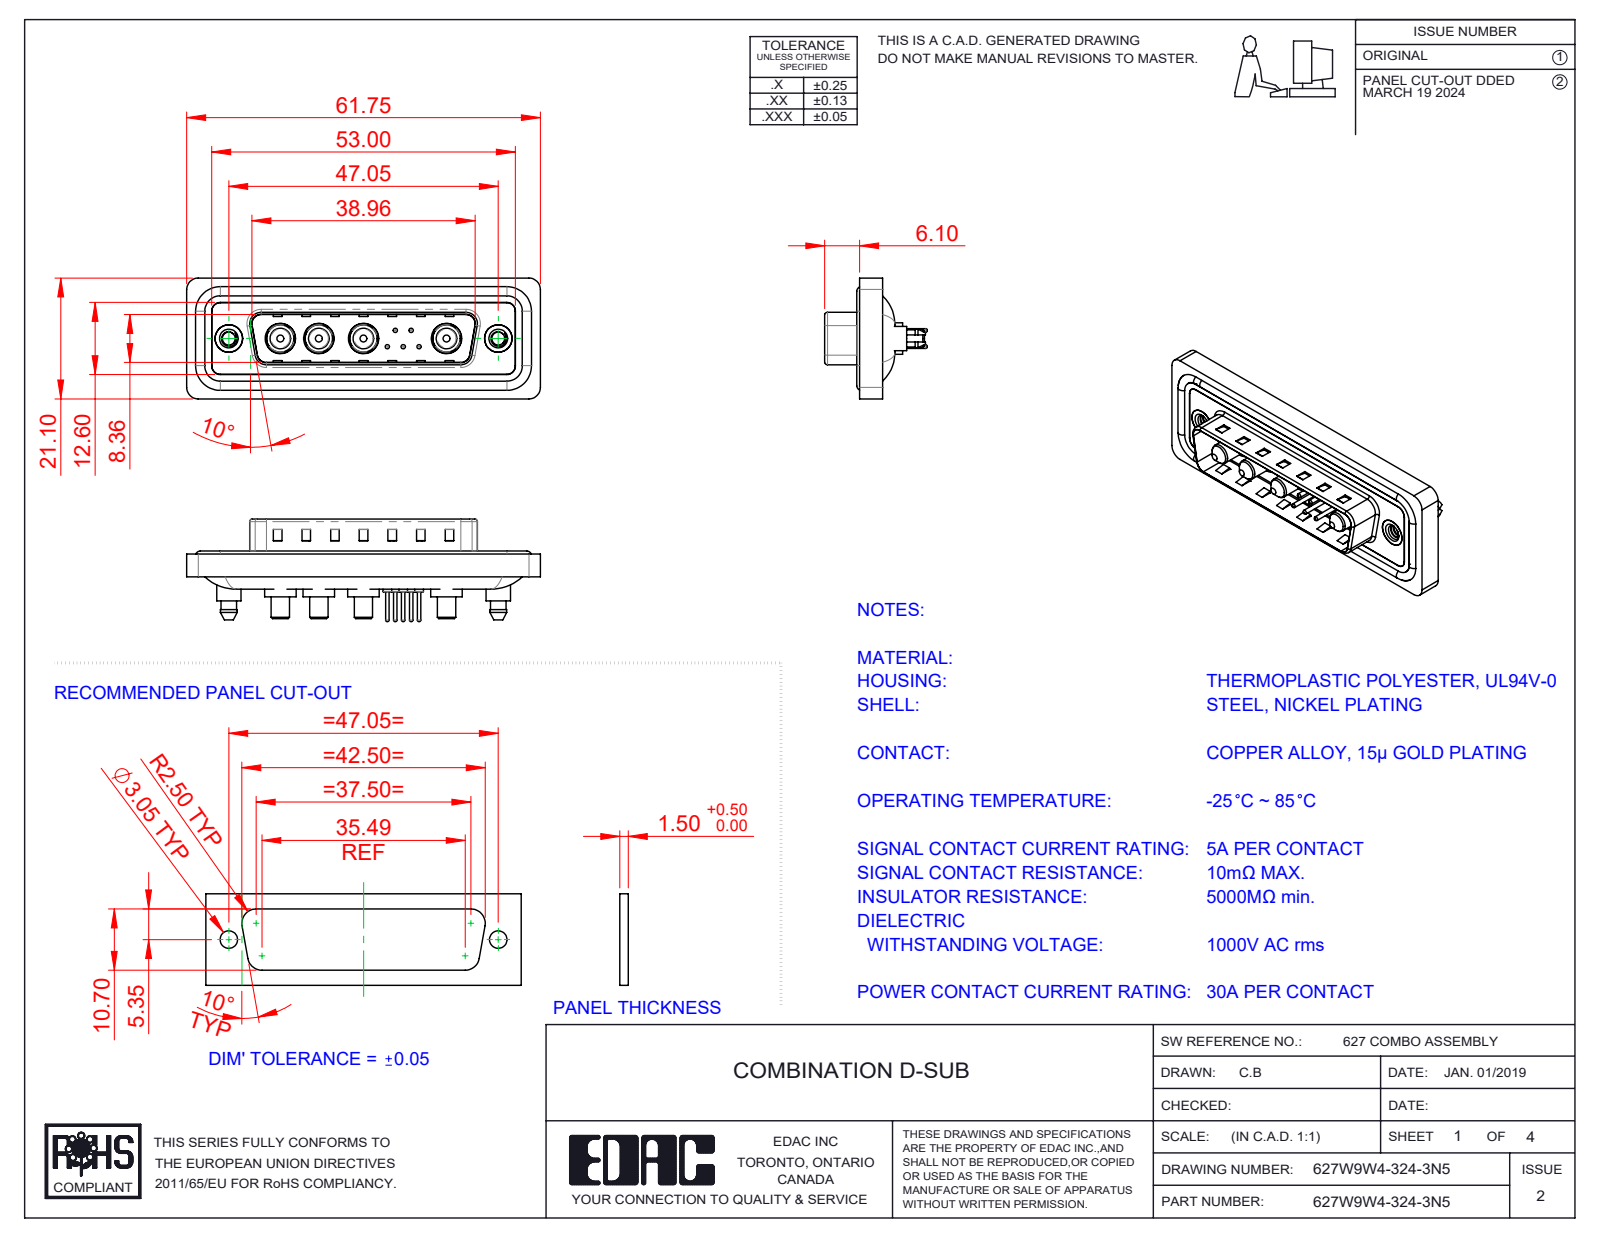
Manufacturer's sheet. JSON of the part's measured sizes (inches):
{"part_name": "Power Pin_30A S; 627Combo Shell Rear_25 Contacts; 627W9W4-324-3N5; 627Combo Contact Row 1_24 (+5 more)", "step_written_by": "SolidWorks 2023 (CONFIG_CONTROL_DESIGN)", "units": "inches", "bodies": {"solids": 20, "faces": 874, "planar": 300, "cylindrical": 366, "other": 208}, "overall_size": [2.431, 0.831, 0.705], "volume_in3": 0.462, "surface_area_in2": 18.89, "round_holes": [[0.03, 5], [0.063, 5], [0.079, 5], [0.191, 4], [0.209, 4], [0.089, 2], [0.157, 2], [0.189, 2], [0.197, 2]], "round_bosses_or_shafts": [[0.059, 5], [0.024, 5], [0.217, 4], [0.205, 4], [0.187, 4], [0.148, 4], [0.142, 4], [0.126, 4]], "partial_cylinders_radius": [[0.059, 24], [0.079, 18], [0.063, 10], [0.02, 8], [0.01, 4], [0.024, 4], [0.026, 4], [0.035, 4]], "face_to_face_distances": [0.016, 0.059, 0.043, 0.02, 0.122, 0.063, 0.114, 0.032, 0.377, 0.222], "hole_center_spacings": [0.124, 0.109, 0.198, 0.571, 0.109, 0.173, 0.174, 0.197]}
